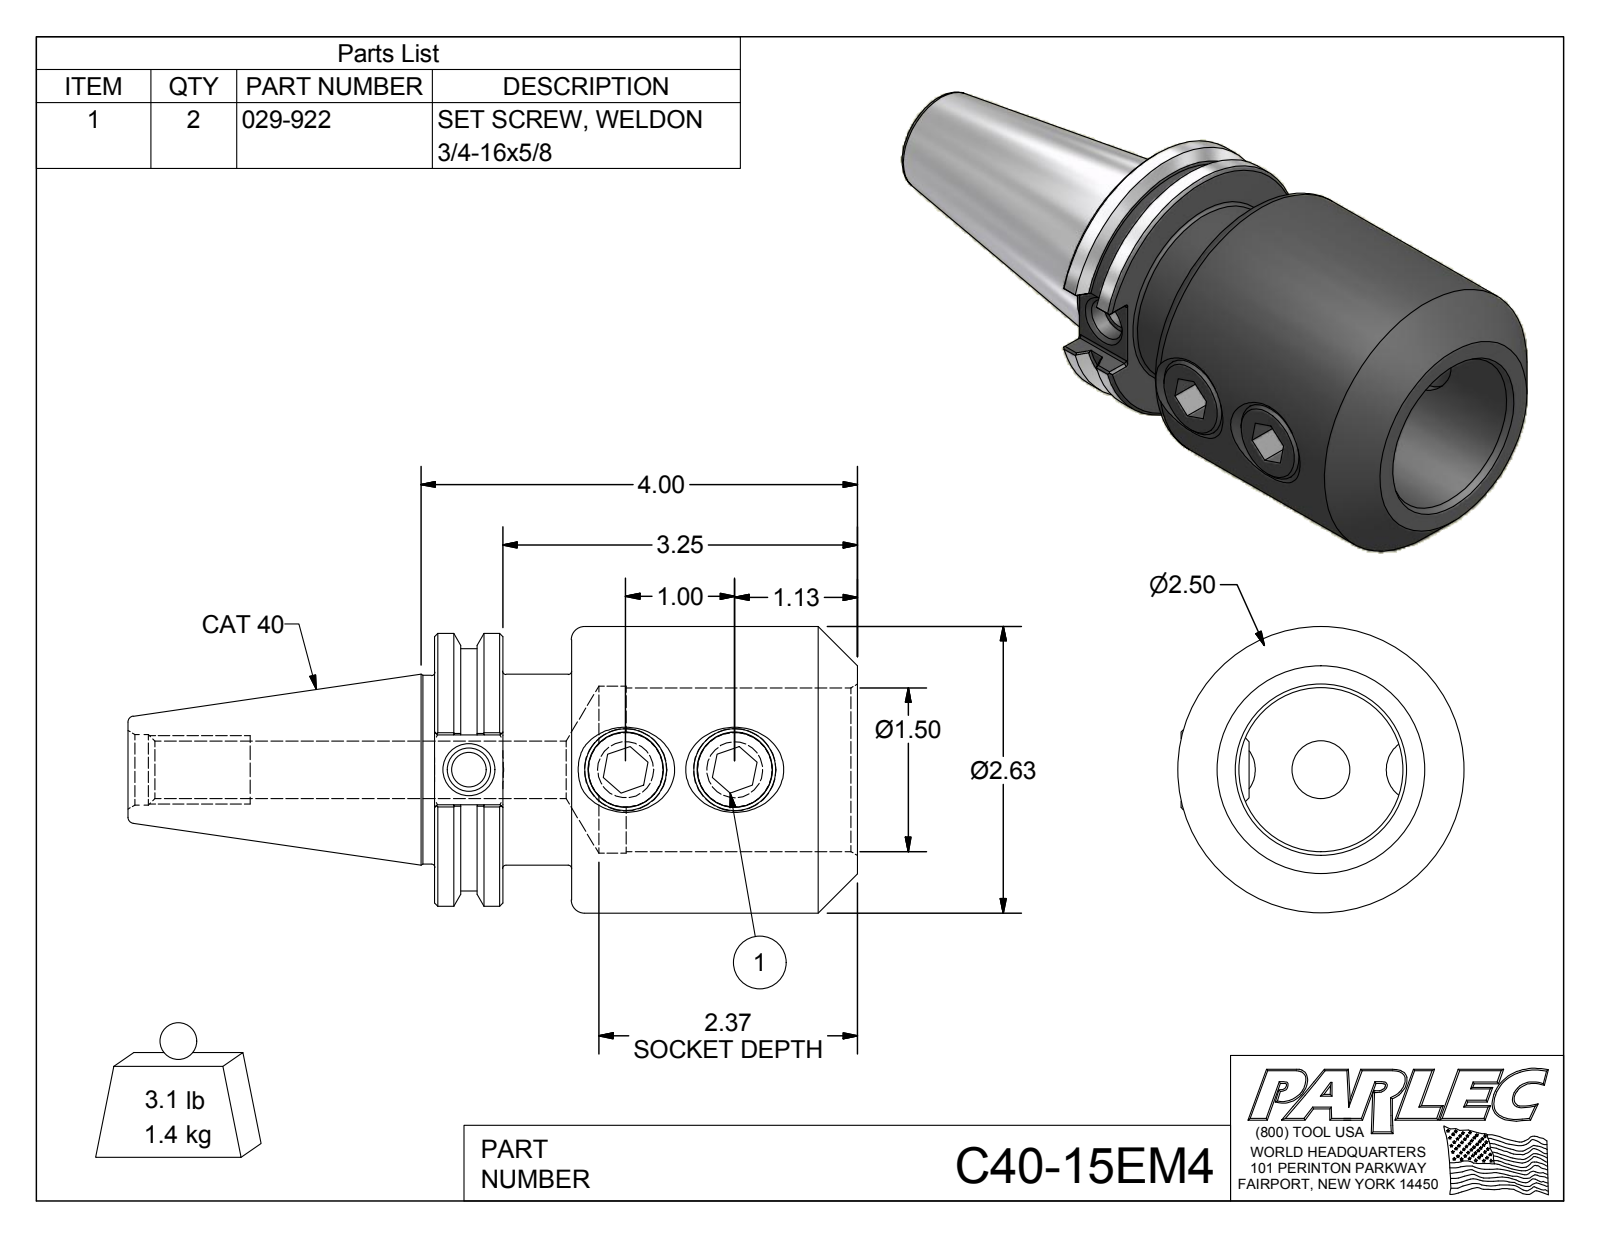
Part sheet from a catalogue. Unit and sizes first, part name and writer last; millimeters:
Units: millimetres
Overall size (bounding box): 169.8 × 66.7 × 66.7
Round holes (diameter × count): ⌀17.4 ×2, ⌀8 ×1, ⌀10.1 ×1, ⌀13.4 ×1, ⌀16.5 ×1, ⌀38.1 ×1, ⌀38.9 ×1
Round bosses / shafts (diameter × count): ⌀19.1 ×2, ⌀66.7 ×1, ⌀63.5 ×1, ⌀56.4 ×1, ⌀44.5 ×1, ⌀43.9 ×1
Partial cylindrical surfaces — rounded edges, fillets, slot ends (radius × count): R0.5 ×12
Main face-to-face distances: 15.9, 31.9, 16, 98.4, 82.6, 66.5, 9.5, 39.2, 55.1, 9.5
Hole centre spacings: 25.4, 36.4, 61.8
Volume: 272 400 mm³ · Surface area: 50 750 mm²
Bodies: 3 solids, 124 faces (52 planar, 34 cylindrical, 38 other)
Part name (STEP PRODUCT): C40-15EM4; C40-15EM4-1; 029-922
STEP written by: Autodesk Inventor 2012 (AUTOMOTIVE_DESIGN)
